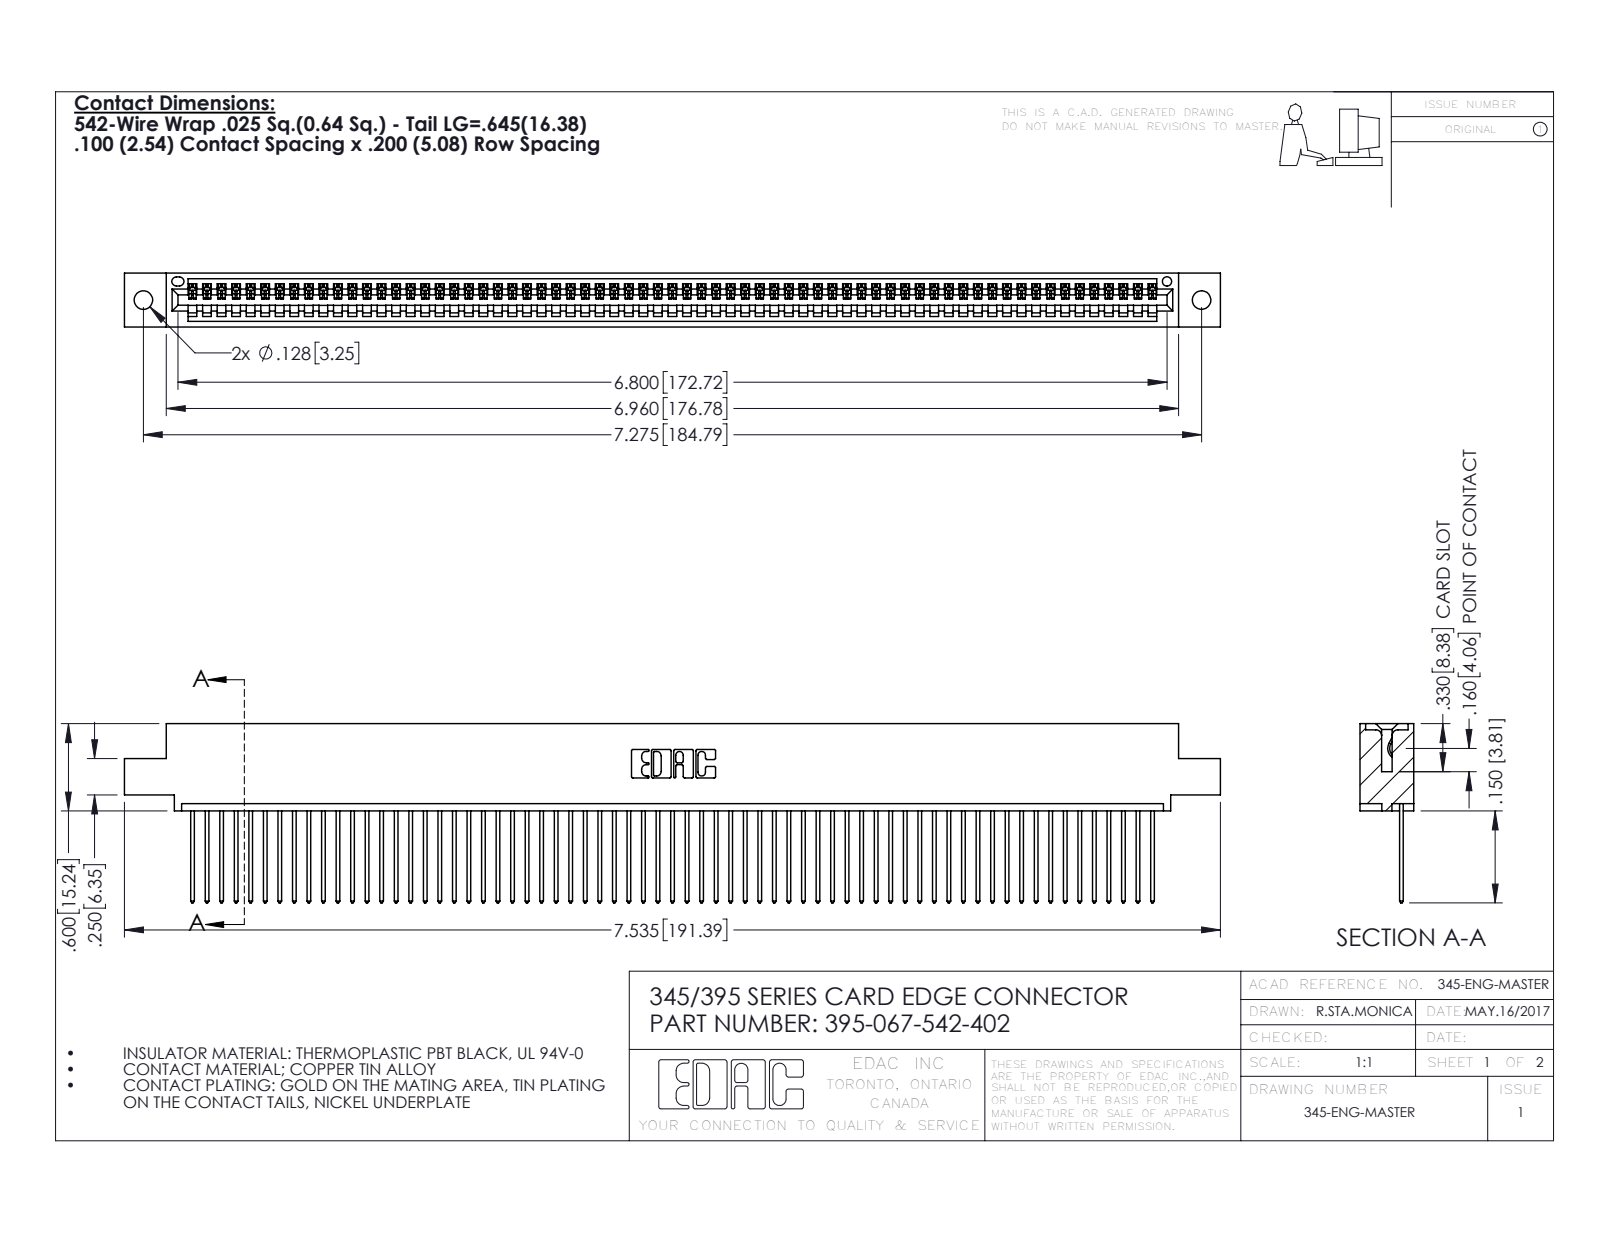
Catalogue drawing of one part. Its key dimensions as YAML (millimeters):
part_name: "345 Part_0.110 Offset - 0.128 Dia; 395-067-542-402; 345-292-001_345-293-142"
step_written_by: "SolidWorks 2016 (CONFIG_CONTROL_DESIGN)"
units: millimeters
bodies: {solids: 68, faces: 4016, planar: 2764, cylindrical: 1252, other: 0}
overall_size: [191.4, 31.3, 9.4]
volume: 18420
surface_area: 25570
round_holes:
  - {diameter: 3.3, count: 2}
  - {diameter: 1.6, count: 1}
partial_cylinders:
  - {radius: 0.2, count: 134}
  - {radius: 0.3, count: 134}
  - {radius: 0.3, count: 22}
  - {radius: 0.2, count: 6}
  - {radius: 0.8, count: 6}
  - {radius: 0.7, count: 3}
  - {radius: 0.8, count: 2}
  - {radius: 1, count: 2}
face_to_face_distances: [1.8, 7.6, 2.5, 6.9, 0.6, 9.4, 5.1, 5.7, 3.8, 1.8]
hole_center_spacings: [6.9, 178.8, 184.8]
